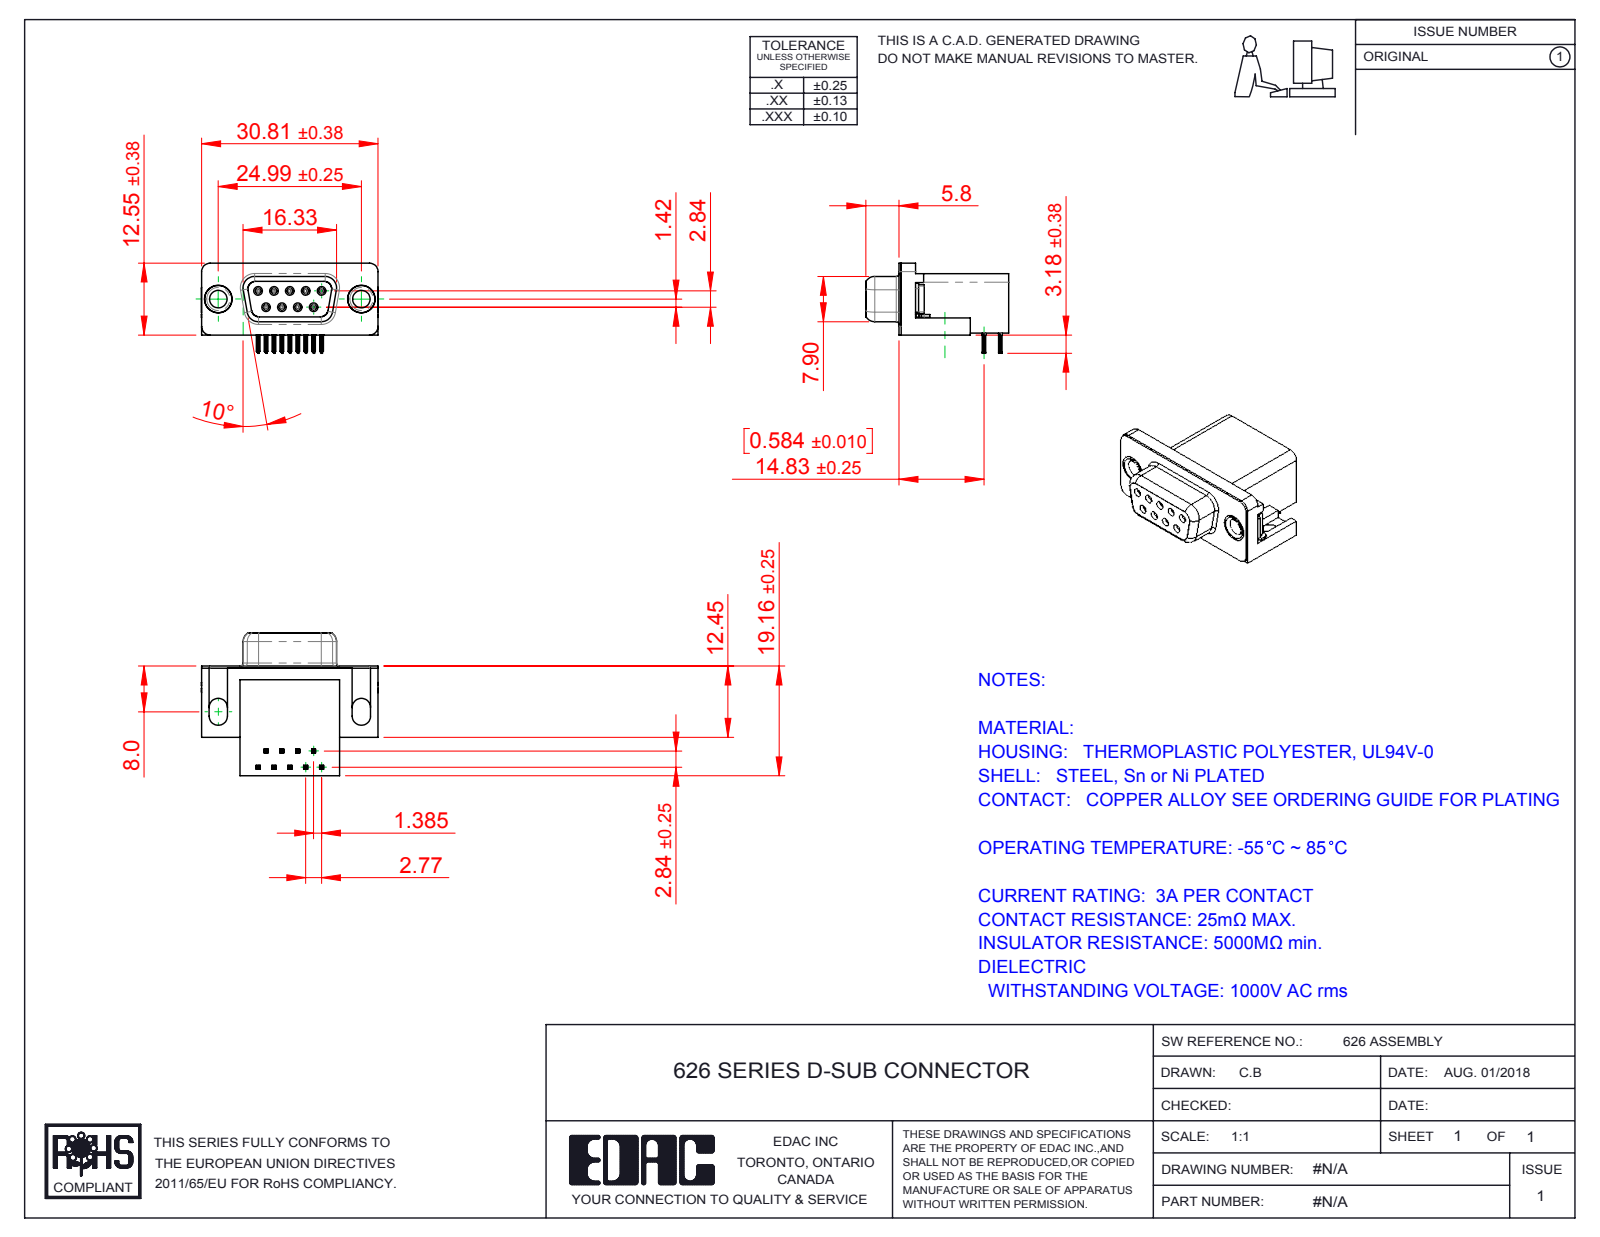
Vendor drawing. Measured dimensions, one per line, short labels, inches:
name: 626 Shell_9 Socket; 626 Thru Hole Rivet; 626 Contact Bottom; 626 Contact Top (+3 more)
written by: SolidWorks 2016 (CONFIG_CONTROL_DESIGN)
unit: in
bodies: 15 solids, 1530 faces (686 planar, 394 cylindrical, 450 other)
size: 1.216 × 0.983 × 0.619
volume: 0.301 in³; area: 8.731 in²
holes: 9× ⌀0.031, 9× ⌀0.035, 2× ⌀0.12, 2× ⌀0.157, 2× ⌀0.189, 2× ⌀0.197
bosses: 9× ⌀0.047, 2× ⌀0.193, 2× ⌀0.187, 2× ⌀0.152
rounds: 72× R0.004, 36× R0.006, 18× R0.014, 18× R0.039, 9× R0.013, 8× R0.01, 8× R0.053, 8× R0.063
face distances: 0.016, 0.407, 0.739, 0.754, 0.114, 0.014, 0.098, 0.244, 0.64, 0.421
hole spacings: 0.124, 0.109, 0.218, 0.198, 0.198, 0.327, 0.294, 0.295
